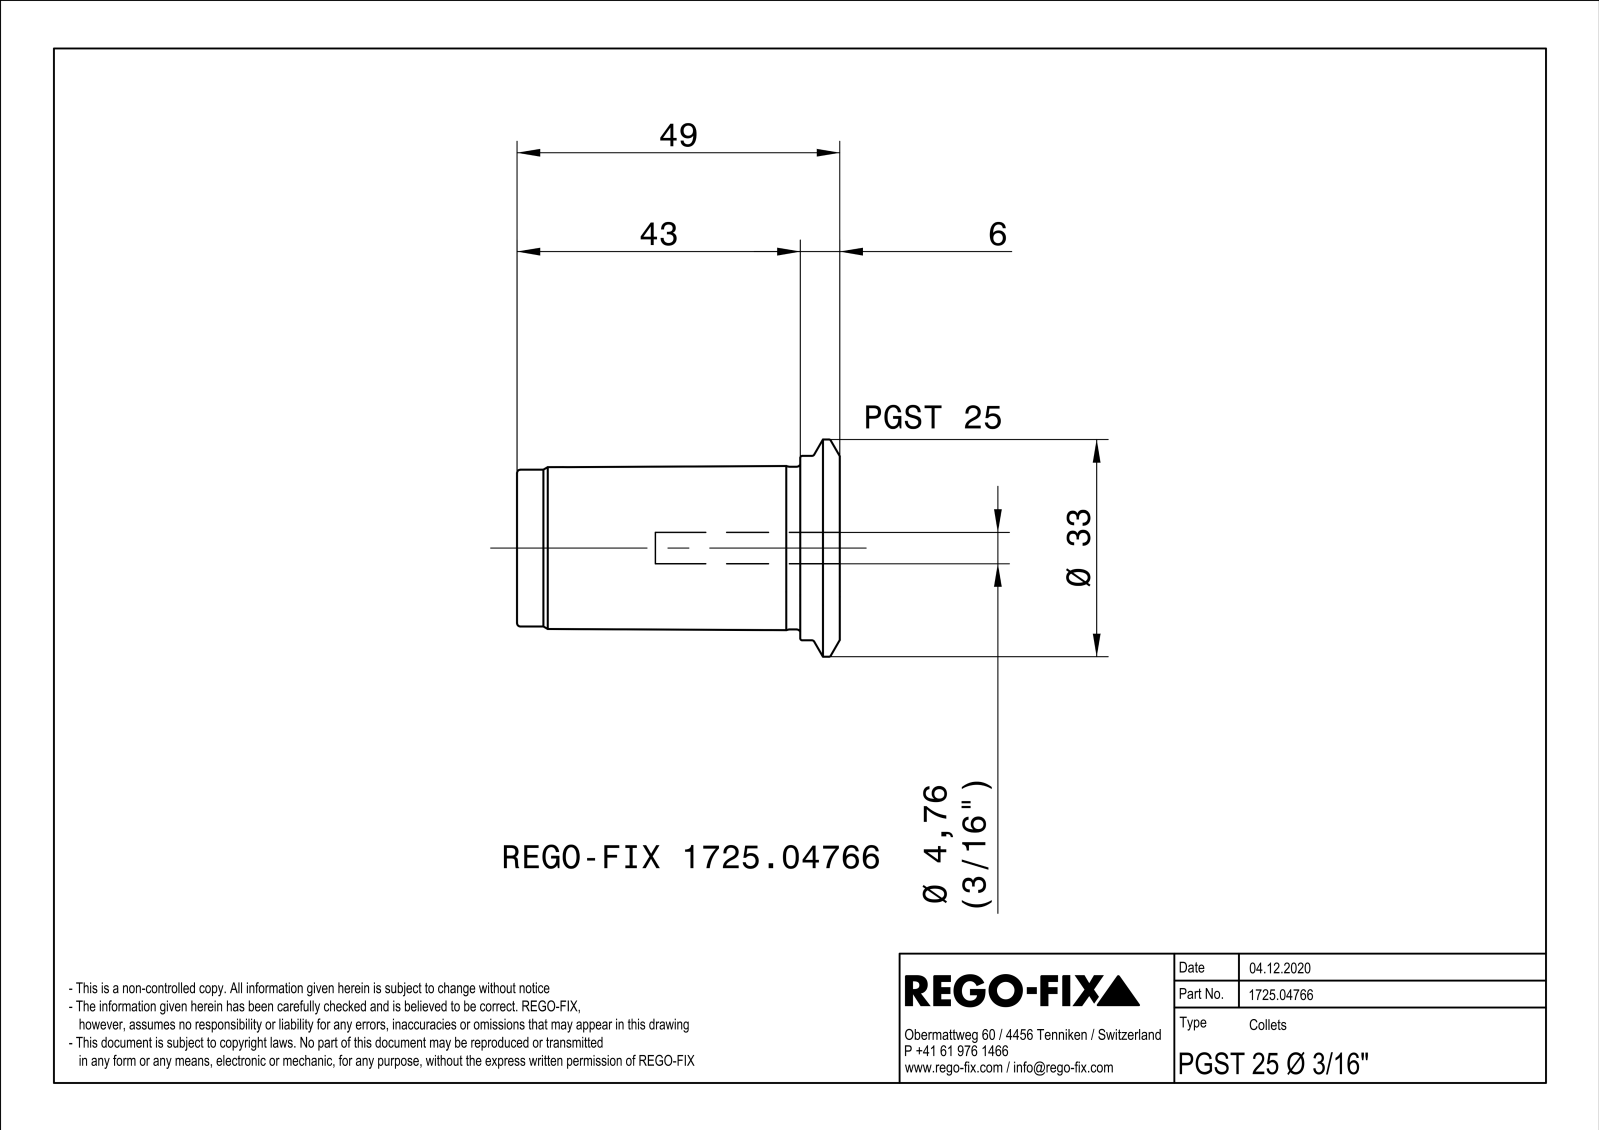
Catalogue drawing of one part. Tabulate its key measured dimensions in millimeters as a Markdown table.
| quantity | value |
| --- | --- |
| part name | NOCUT |
| STEP written by | SIEMENS PLM Software Solid Edge ST10 (AUTOMOTIVE_DESIGN) |
| units | millimeters |
| bodies | 2 solids, 56 faces (14 planar, 18 cylindrical, 24 other) |
| overall size | 49 × 32.98 × 32.98 |
| volume | 23 131 mm³ |
| surface area | 8 005 mm² |
| round holes (diameter × count) | 3 × 4, 1.5 × 1, 4.76 × 1, 5.2 × 1, 17 × 1, 21.19 × 1, 22.3 × 1 |
| round bosses / shafts (diameter × count) | 32.98 × 1, 28 × 1, 24.7 × 1, 23.8 × 1, 22 × 1, 21 × 1, 5 × 1, 2.8 × 1 |
| main face-to-face distances | 43.5, 49, 5.5, 6, 37.5, 43, 28, 22, 15.5, 21 |
| hole center spacings | 6.5, 11.26 |
